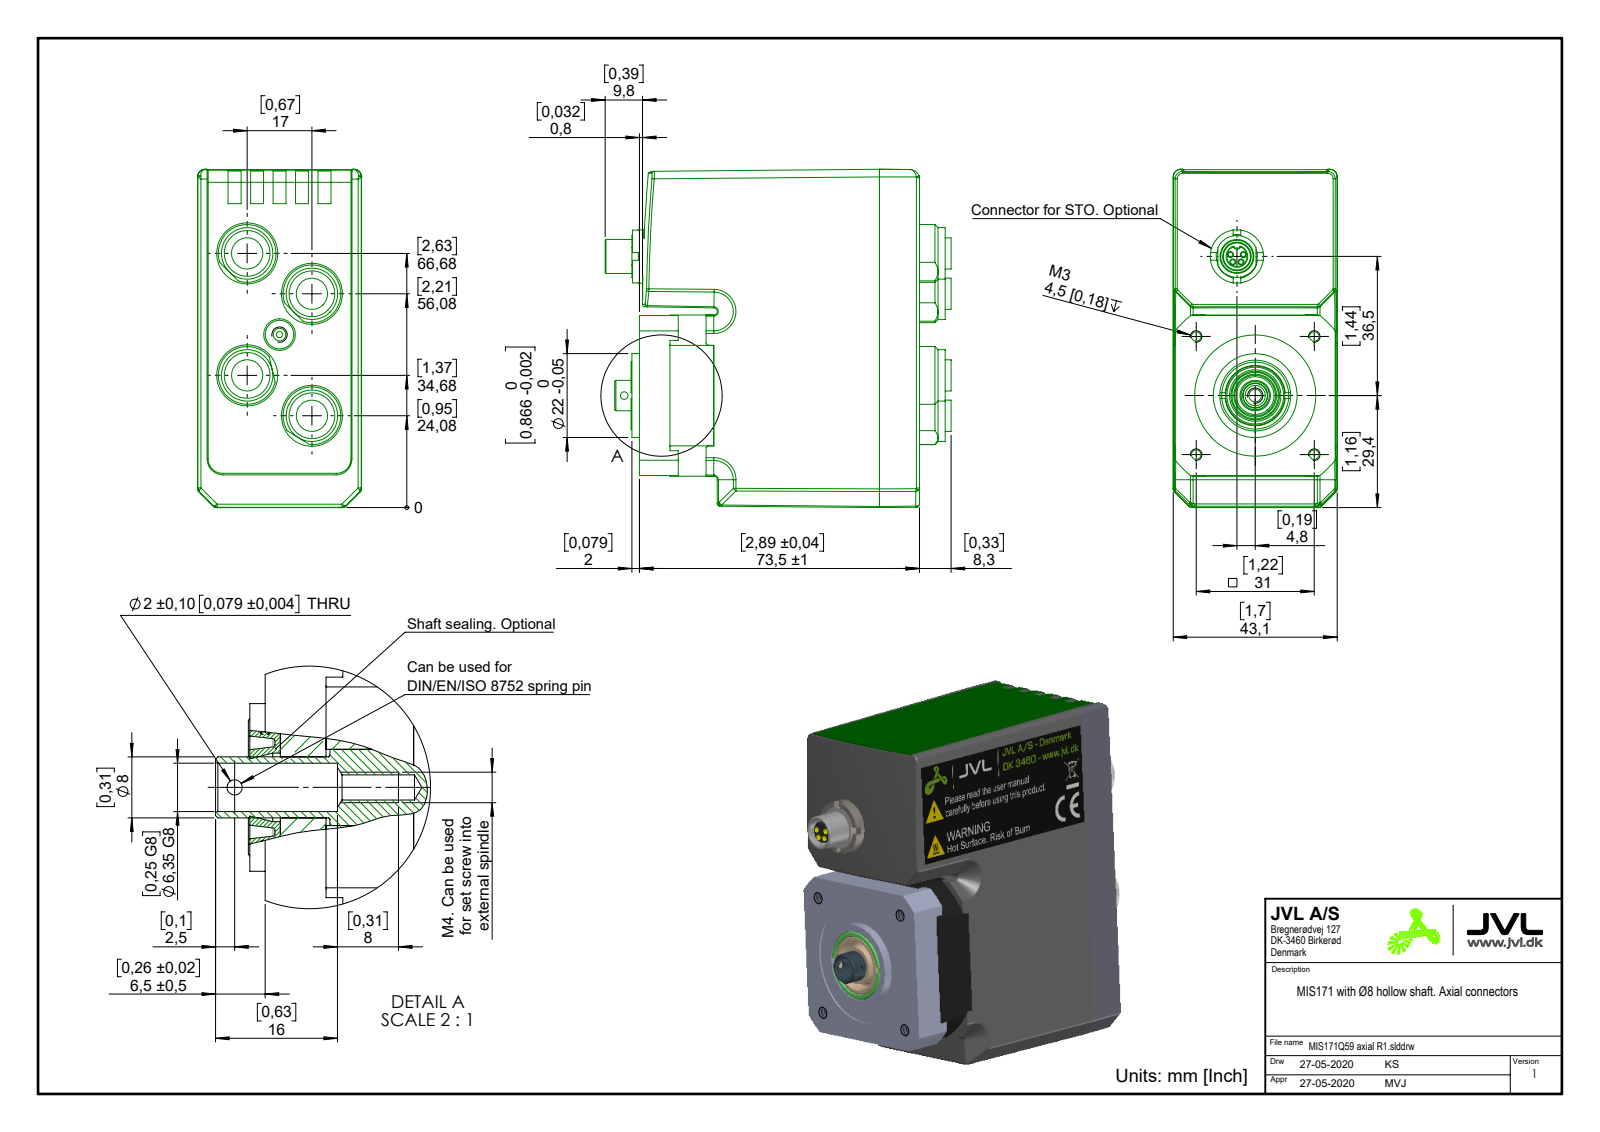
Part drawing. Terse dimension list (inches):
name: MIS171Q59 axial R1
written by: SolidWorks 2018 (AUTOMOTIVE_DESIGN)
unit: in
bodies: 3 solids, 633 faces (255 planar, 234 cylindrical, 144 other)
size: 3.575 × 3.494 × 1.695
volume: 16.23 in³; area: 52.51 in²
holes: 4× ⌀0.047, 4× ⌀0.098, 4× ⌀0.472, 4× ⌀0.63, 2× ⌀0.13, 1× ⌀0.079, 1× ⌀0.25, 1× ⌀0.28, 1× ⌀0.327, 1× ⌀0.354, 1× ⌀0.394, 1× ⌀1.252
bosses: 4× ⌀0.596, 4× ⌀0.531, 4× ⌀0.323, 4× ⌀0.063, 4× ⌀0.031, 1× ⌀0.866, 1× ⌀0.61, 1× ⌀0.551
rounds: 30× R0.039, 4× R0.031, 2× R0.008, 2× R0.037, 2× R0.079, 2× R0.15, 2× R0.165, 1× R0.014
face distances: 1.696, 1.659, 2.89, 0.079, 1.665, 2.894, 1.654, 0.02, 2.87, 2.874
hole spacings: 0.863, 1.22, 0.07, 0.081, 0.134, 0.394, 0.487, 0.538
